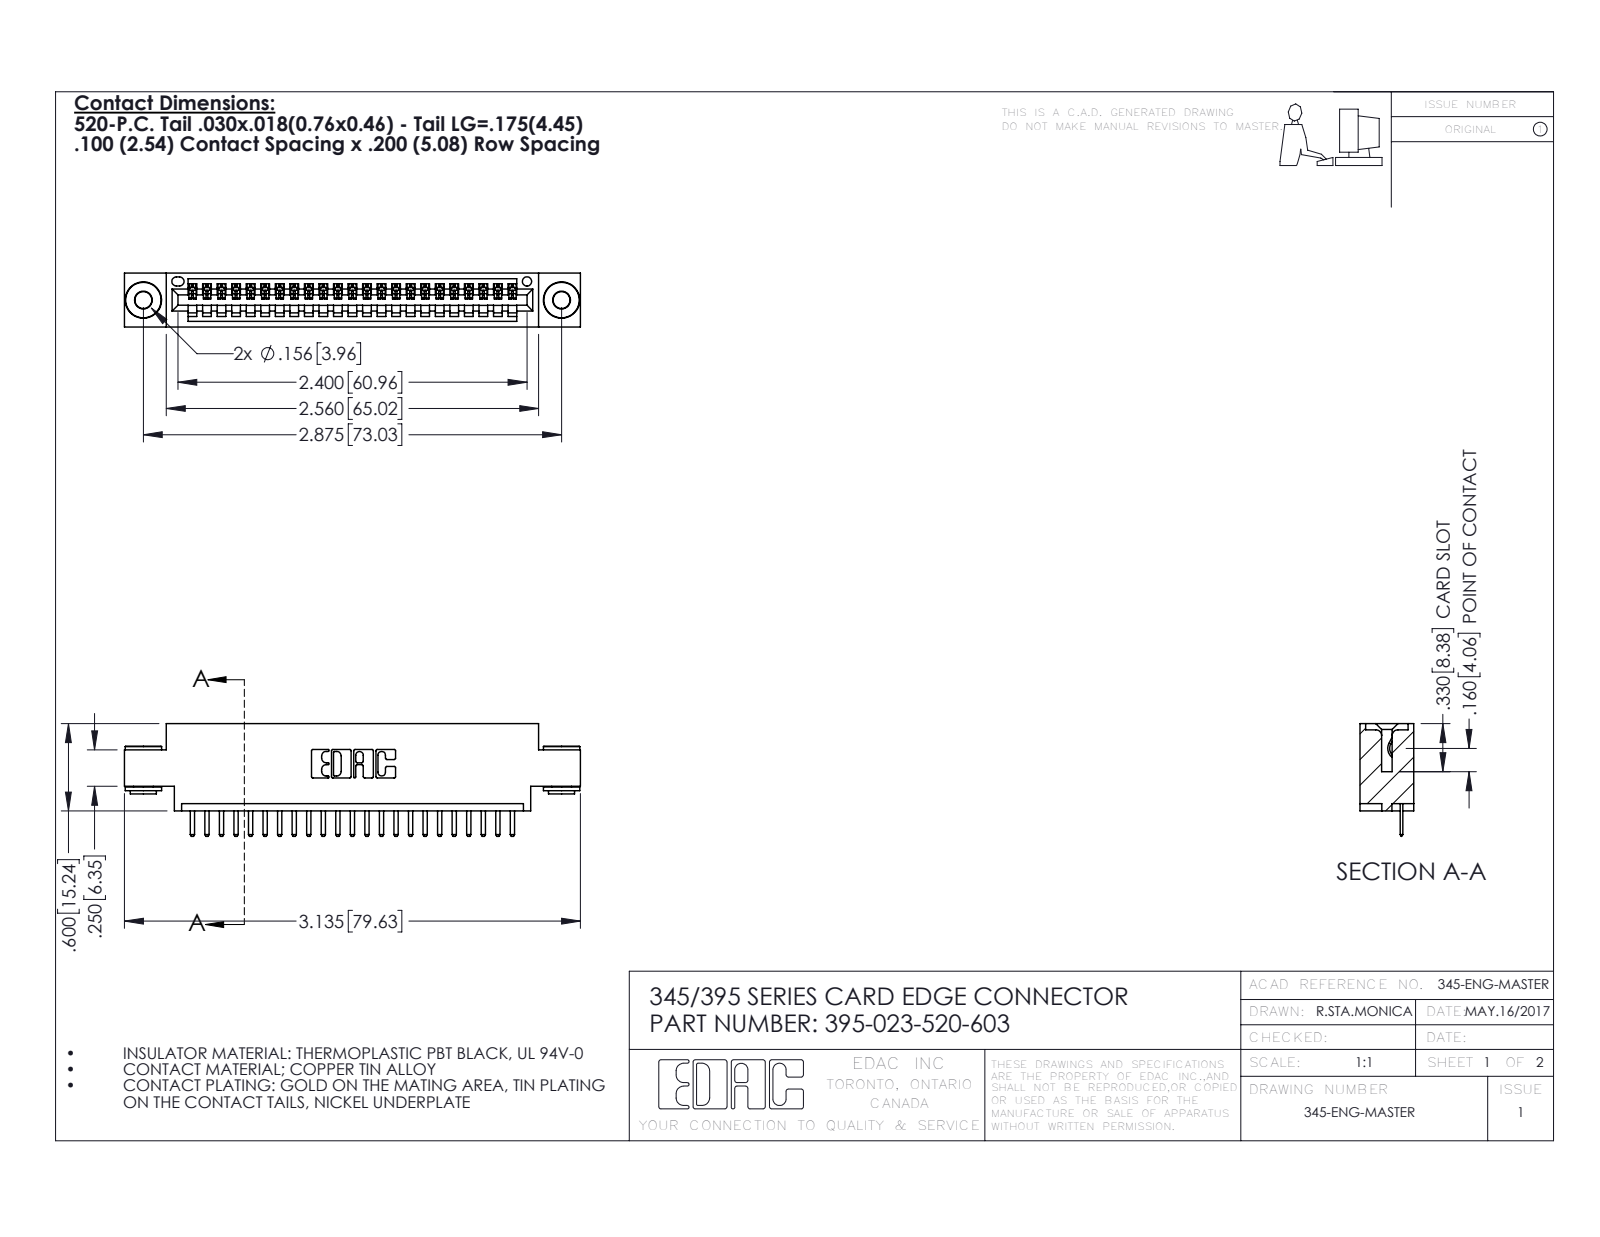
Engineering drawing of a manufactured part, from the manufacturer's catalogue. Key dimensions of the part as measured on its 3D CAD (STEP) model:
Part name (STEP PRODUCT): 395-023-520-603; 345-292-001_345-293-120; 345 Part_0.170 Offset - 0.156 Dia-TH; 345-250-002_345-250-002-102
STEP written by: SolidWorks 2016 (CONFIG_CONTROL_DESIGN)
Units: inches
Bodies: 26 solids, 1594 faces (1060 planar, 526 cylindrical, 8 other)
Overall size (bounding box): 3.135 × 0.775 × 0.37
Volume: 0.442 in³ · Surface area: 14.72 in²
Round holes (diameter × count): ⌀0.116 ×2, ⌀0.156 ×2, ⌀0.064 ×1
Round bosses / shafts (diameter × count): ⌀0.25 ×2, ⌀0.18 ×2, ⌀0.136 ×2
Partial cylindrical surfaces — rounded edges, fillets, slot ends (radius × count): R0.01 ×48, R0.006 ×46, R0.01 ×22, R0.007 ×6, R0.031 ×6, R0.026 ×3, R0.031 ×2, R0.04 ×2
Main face-to-face distances: 0.37, 0.072, 0.298, 0.2, 0.098, 0.272, 0.025, 0.225, 0.175, 0.072
Hole centre spacings: 0.27, 2.641, 2.875
